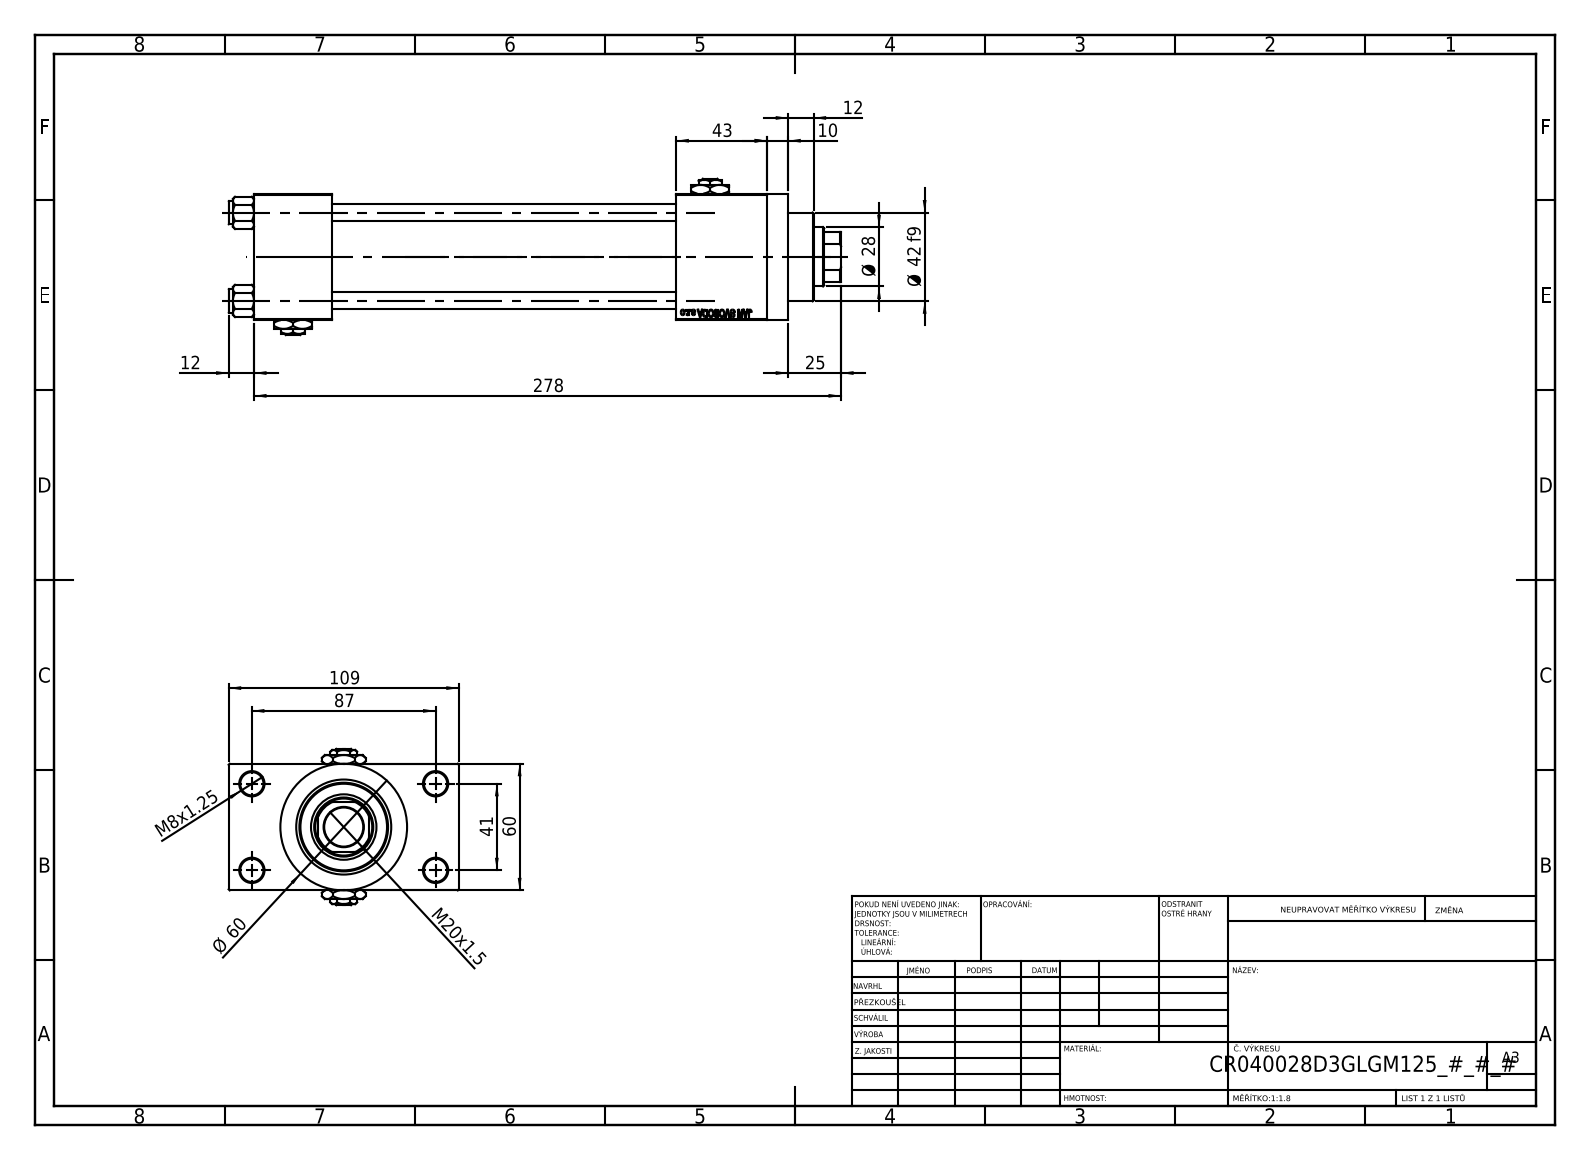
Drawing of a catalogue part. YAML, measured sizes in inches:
part_name: "Zatka_pro_OIL_PORT; NUT_M5_D; V215CR_D_Body; V215_VC_A (+2 more)"
step_written_by: "SolidWorks 2019 (CONFIG_CONTROL_DESIGN)"
units: inches
bodies: {solids: 13, faces: 1189, planar: 542, cylindrical: 89, other: 558}
overall_size: [11.417, 4.291, 2.913]
volume: 40.6
surface_area: 275.6
round_holes:
  - {diameter: 0.315, count: 4}
  - {diameter: 0.433, count: 4}
  - {diameter: 0.276, count: 2}
  - {diameter: 0.656, count: 2}
  - {diameter: 0.945, count: 2}
  - {diameter: 0.728, count: 1}
  - {diameter: 1.102, count: 1}
  - {diameter: 1.22, count: 1}
  - {diameter: 1.575, count: 1}
  - {diameter: 1.772, count: 1}
round_bosses_or_shafts:
  - {diameter: 0.433, count: 4}
  - {diameter: 2.362, count: 1}
  - {diameter: 1.811, count: 1}
  - {diameter: 1.654, count: 1}
partial_cylinders:
  - {radius: 0.531, count: 1}
face_to_face_distances: [2.362, 0.965, 3.327, 6.417, 1.457, 7.874, 9.567, 8.11, 1.693, 4.291]
hole_center_spacings: [0.892, 1.161, 1.642, 1.856, 1.893, 2.533, 3.011, 1.614]
